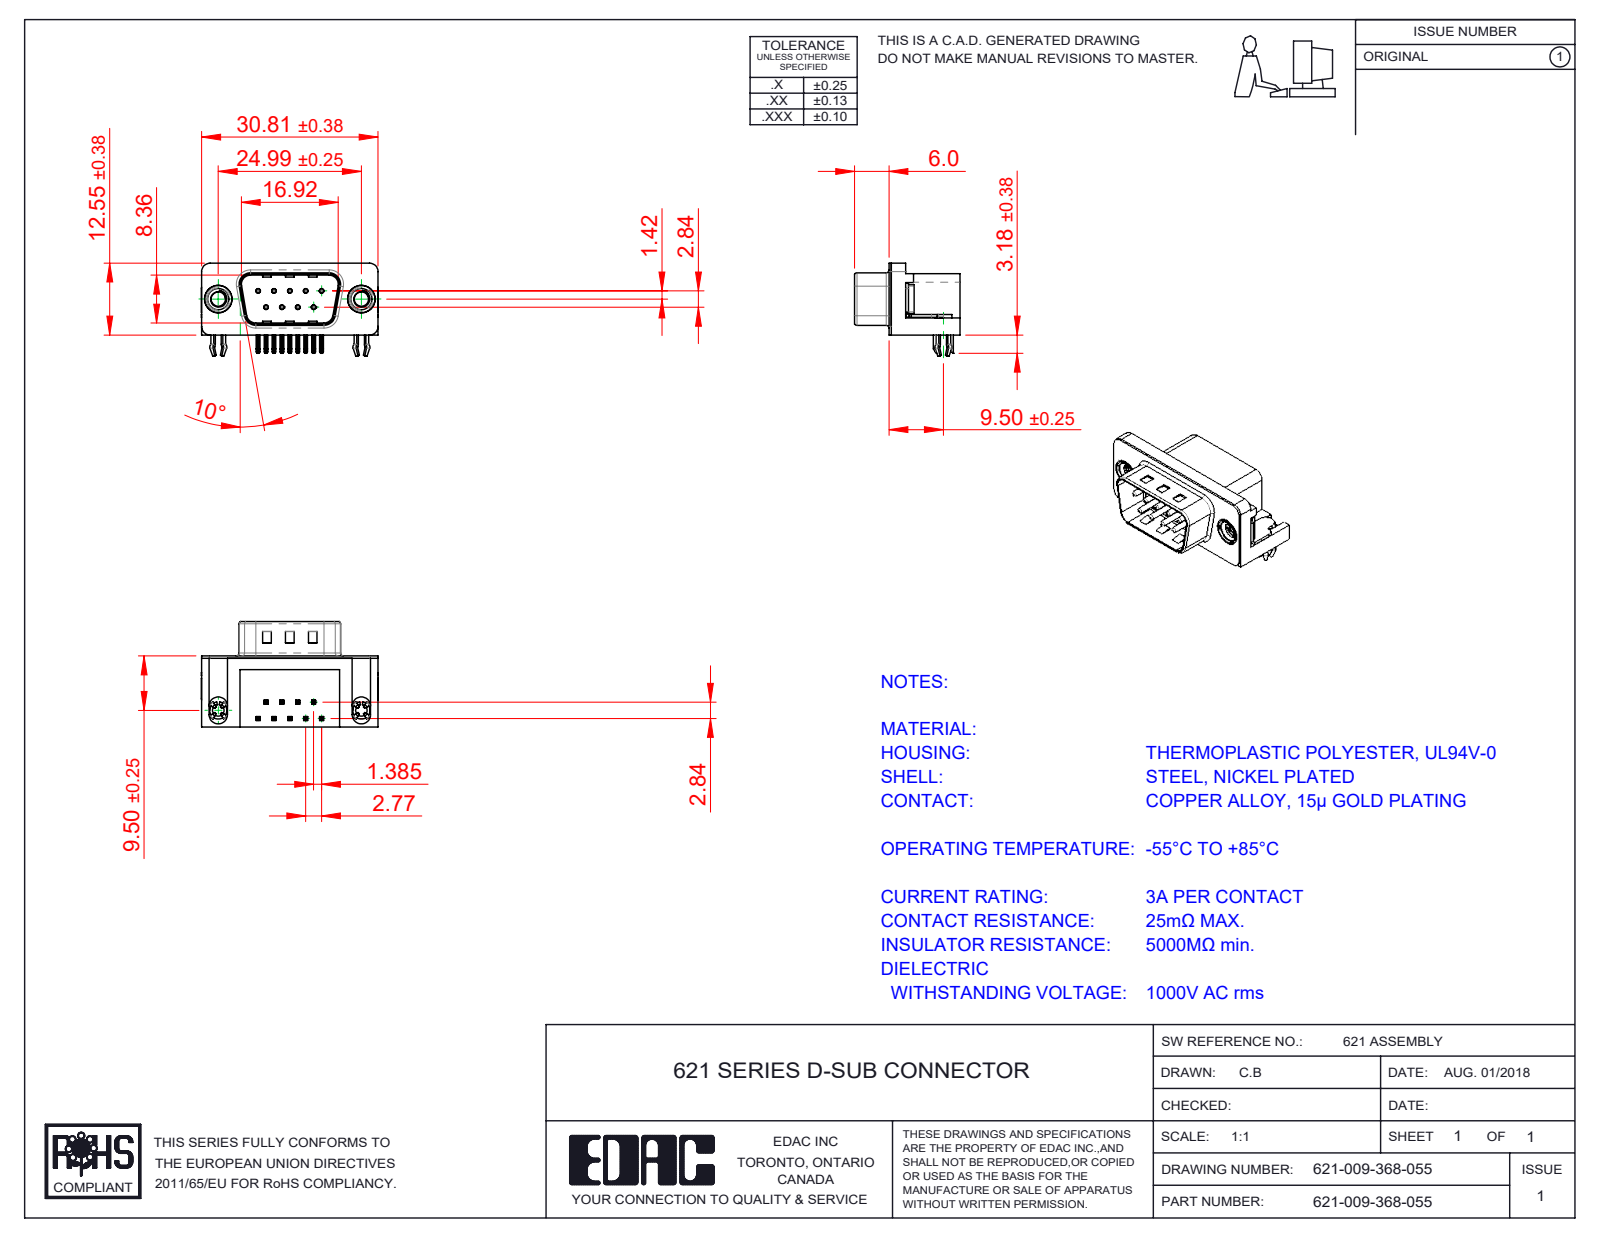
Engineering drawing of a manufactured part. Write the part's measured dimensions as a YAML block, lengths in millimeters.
part_name: "621 Contact Top; 621 Contact Bottom; 621-009-368-055; 621 Shell_9 Socket (+3 more)"
step_written_by: "SolidWorks 2016 (CONFIG_CONTROL_DESIGN)"
units: millimeters
bodies: {solids: 15, faces: 1021, planar: 573, cylindrical: 331, other: 117}
overall_size: [30.89, 18.4, 15.73]
volume: 3252
surface_area: 4503
round_holes:
  - {diameter: 0.35, count: 9}
  - {diameter: 0.8, count: 9}
  - {diameter: 2.26, count: 2}
  - {diameter: 2.5, count: 2}
  - {diameter: 4, count: 2}
  - {diameter: 4.8, count: 2}
  - {diameter: 5, count: 2}
round_bosses_or_shafts:
  - {diameter: 0.75, count: 9}
  - {diameter: 4.9, count: 2}
  - {diameter: 4.75, count: 2}
  - {diameter: 3.9, count: 2}
  - {diameter: 3.26, count: 2}
partial_cylinders:
  - {radius: 0.25, count: 44}
  - {radius: 0.12, count: 18}
  - {radius: 1, count: 16}
  - {radius: 0.5, count: 9}
  - {radius: 1.5, count: 8}
  - {radius: 1.6, count: 8}
  - {radius: 0.9, count: 4}
  - {radius: 2, count: 4}
face_to_face_distances: [0.4, 12, 12.4, 10.35, 2.9, 9.5, 2.5, 0.5, 2.1, 0.35]
hole_center_spacings: [3.16, 2.77, 5.54, 5.03, 5.04, 8.31, 7.48, 7.49]
